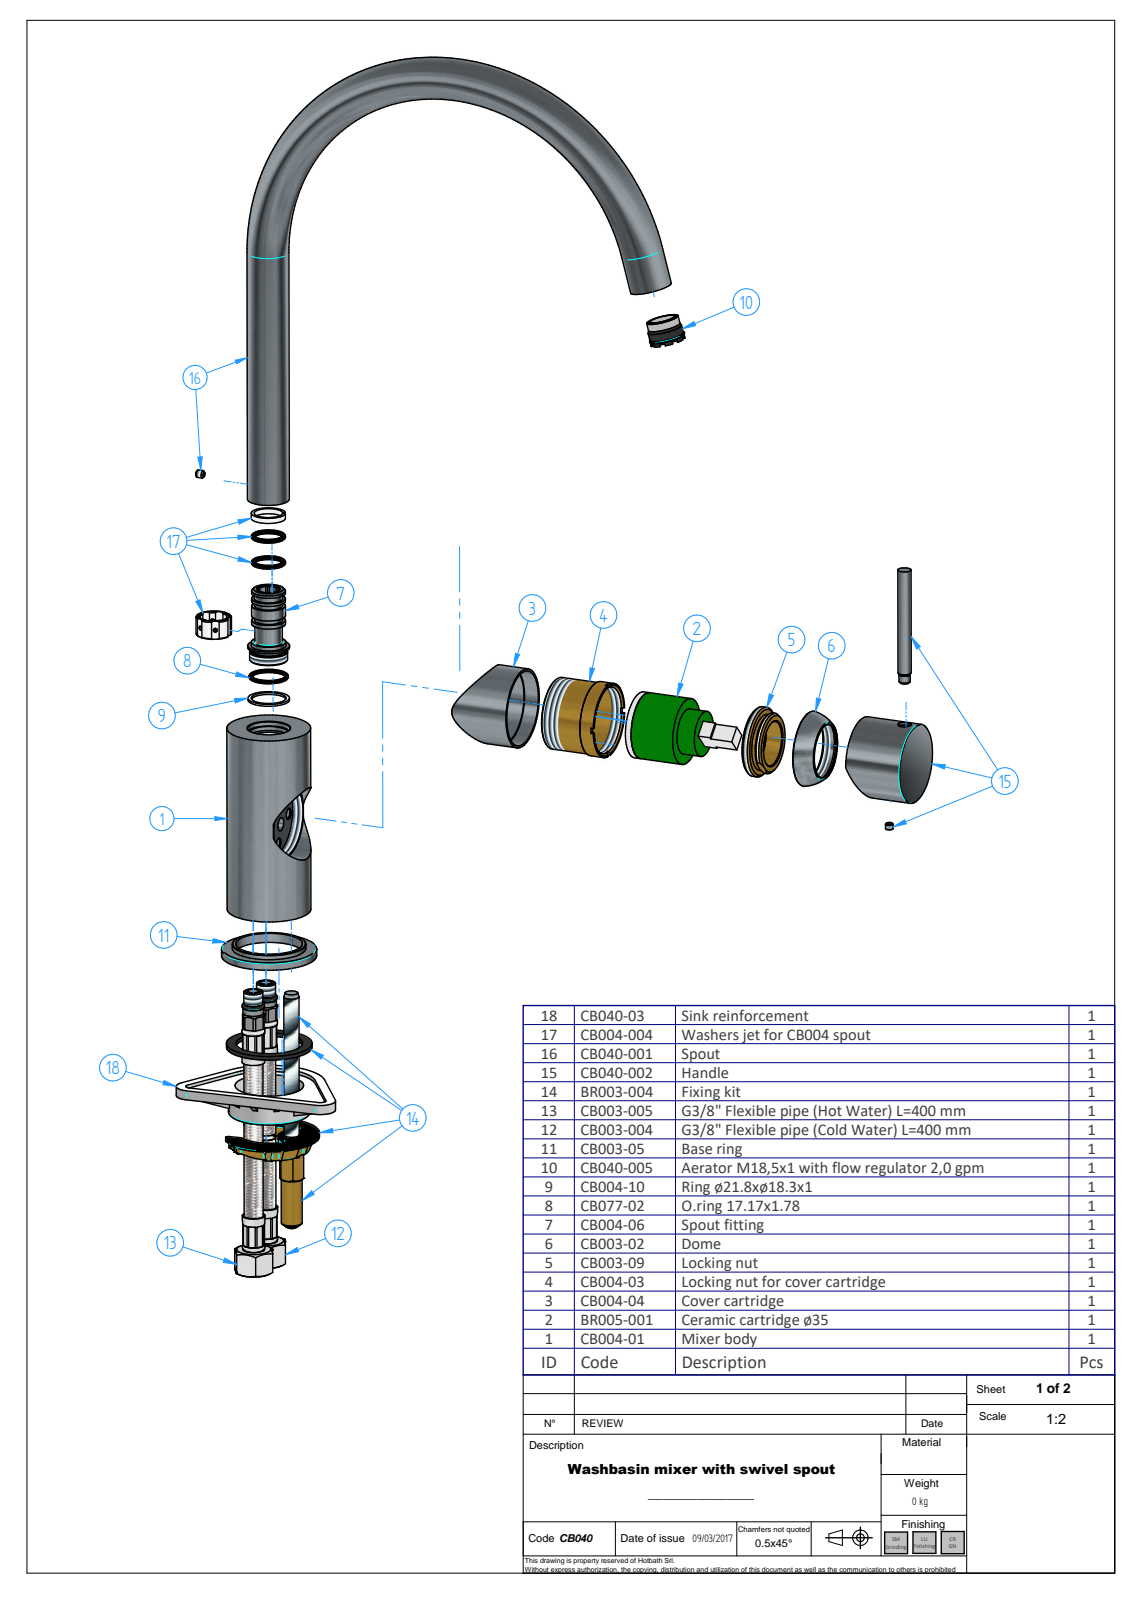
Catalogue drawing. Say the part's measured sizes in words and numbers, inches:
The part is named "CB040-00; CB040-002_oa_0; CB004-05; CB040-02 (+8 more)". Its 3-D file was written by "Solid Edge (AUTOMOTIVE_DESIGN)". It is 9 solids with 1091 faces: 653 planar, 306 cylindrical and 132 other. Overall it measures 14.197 by 10.11 by 3.876 inches. Its volume is 11.21 cubic inches and its surface area 176.6 square inches. Round holes: 116 of diameter 0.03, 4 of diameter 0.197, 4 of diameter 0.236, 3 of diameter 0.315, 3 of diameter 0.433, 2 of diameter 0.354, 2 of diameter 0.709, 2 of diameter 1.535, 1 of diameter 0.13, 1 of diameter 0.165, 1 of diameter 0.262, 1 of diameter 0.268. Round bosses or shafts: 2 of diameter 0.866, 1 of diameter 1.969, 1 of diameter 1.654, 1 of diameter 1.524, 1 of diameter 0.728, 1 of diameter 0.724, 1 of diameter 0.686, 1 of diameter 0.685. Partial cylindrical surfaces (rounded edges, fillets, slot ends): 4 of radius 0.004, 4 of radius 0.433, 2 of radius 0.197, 1 of radius 0.019, 1 of radius 0.256, 1 of radius 0.354, 1 of radius 0.748, 1 of radius 0.783. The main face-to-face distances are 3.031, 3.937, 2.508, 0.906, 1.063, 0.098, 1.004, 4.035, 0.157, 0.059. The hole center spacings are 0.121, 0.121, 0.125, 0.211, 0.092, 0.106, 0.147, 0.151.
